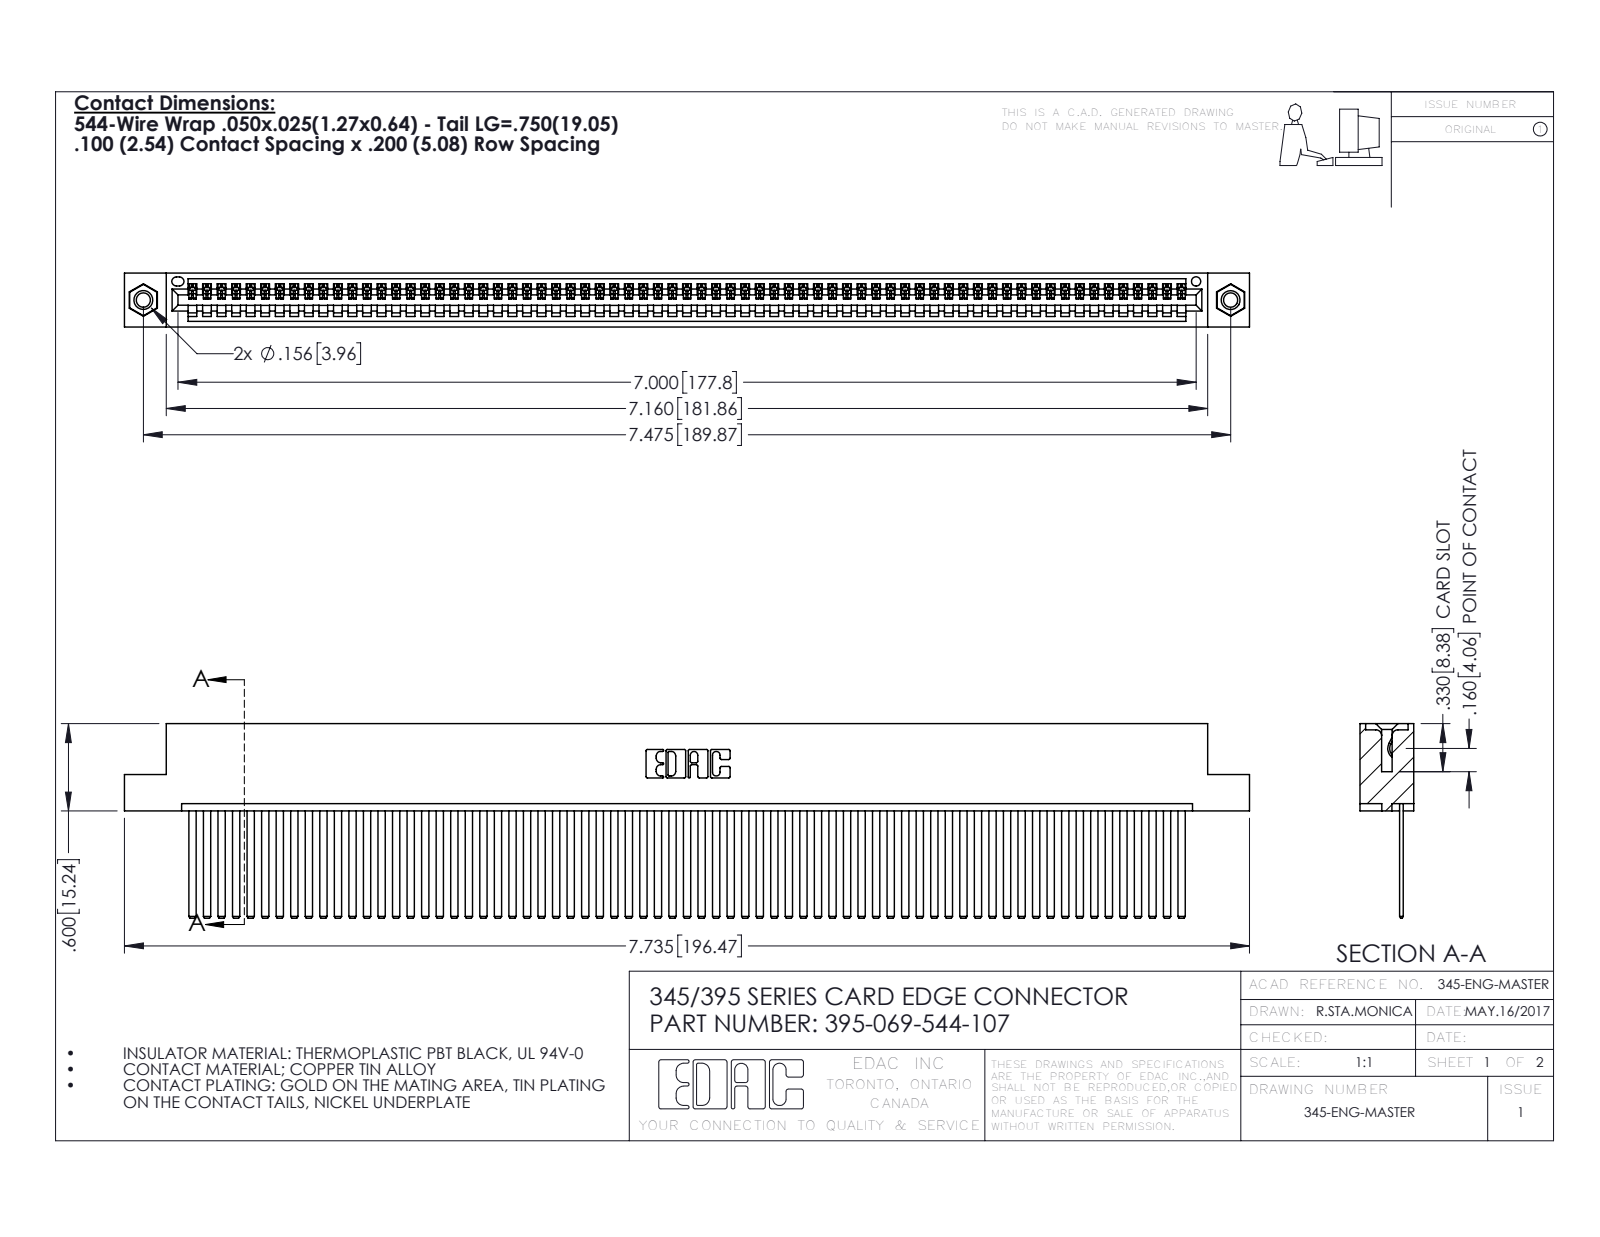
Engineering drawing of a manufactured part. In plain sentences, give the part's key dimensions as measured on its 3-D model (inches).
The part is named "395-069-544-107; 345 Part_Flush Mounting Lugs - 0.156 Dia-TI; 345-292-001_345-293-144; 345-250-001_345-250-005-103". Its 3-D file was written by "SolidWorks 2016 (CONFIG_CONTROL_DESIGN)". It is 72 solids with 3774 faces: 2596 planar, 1162 cylindrical and 16 other. Overall it measures 7.735 by 1.337 by 0.37 inches. Its volume is 1.2 cubic inches and its surface area 44.85 square inches. Round holes: 2 of diameter 0.098, 2 of diameter 0.125, 2 of diameter 0.156, 1 of diameter 0.064. Round bosses or shafts: 2 of diameter 0.155. Partial cylindrical surfaces (rounded edges, fillets, slot ends): 138 of radius 0.006, 22 of radius 0.01, 6 of radius 0.007, 6 of radius 0.031, 3 of radius 0.026, 2 of radius 0.031, 2 of radius 0.04, 1 of radius 0.014. The main face-to-face distances are 0.072, 0.298, 0.025, 0.098, 0.272, 0.37, 0.2, 0.225, 0.149, 0.072. The hole center spacings are 0.27, 7.239, 7.475.
